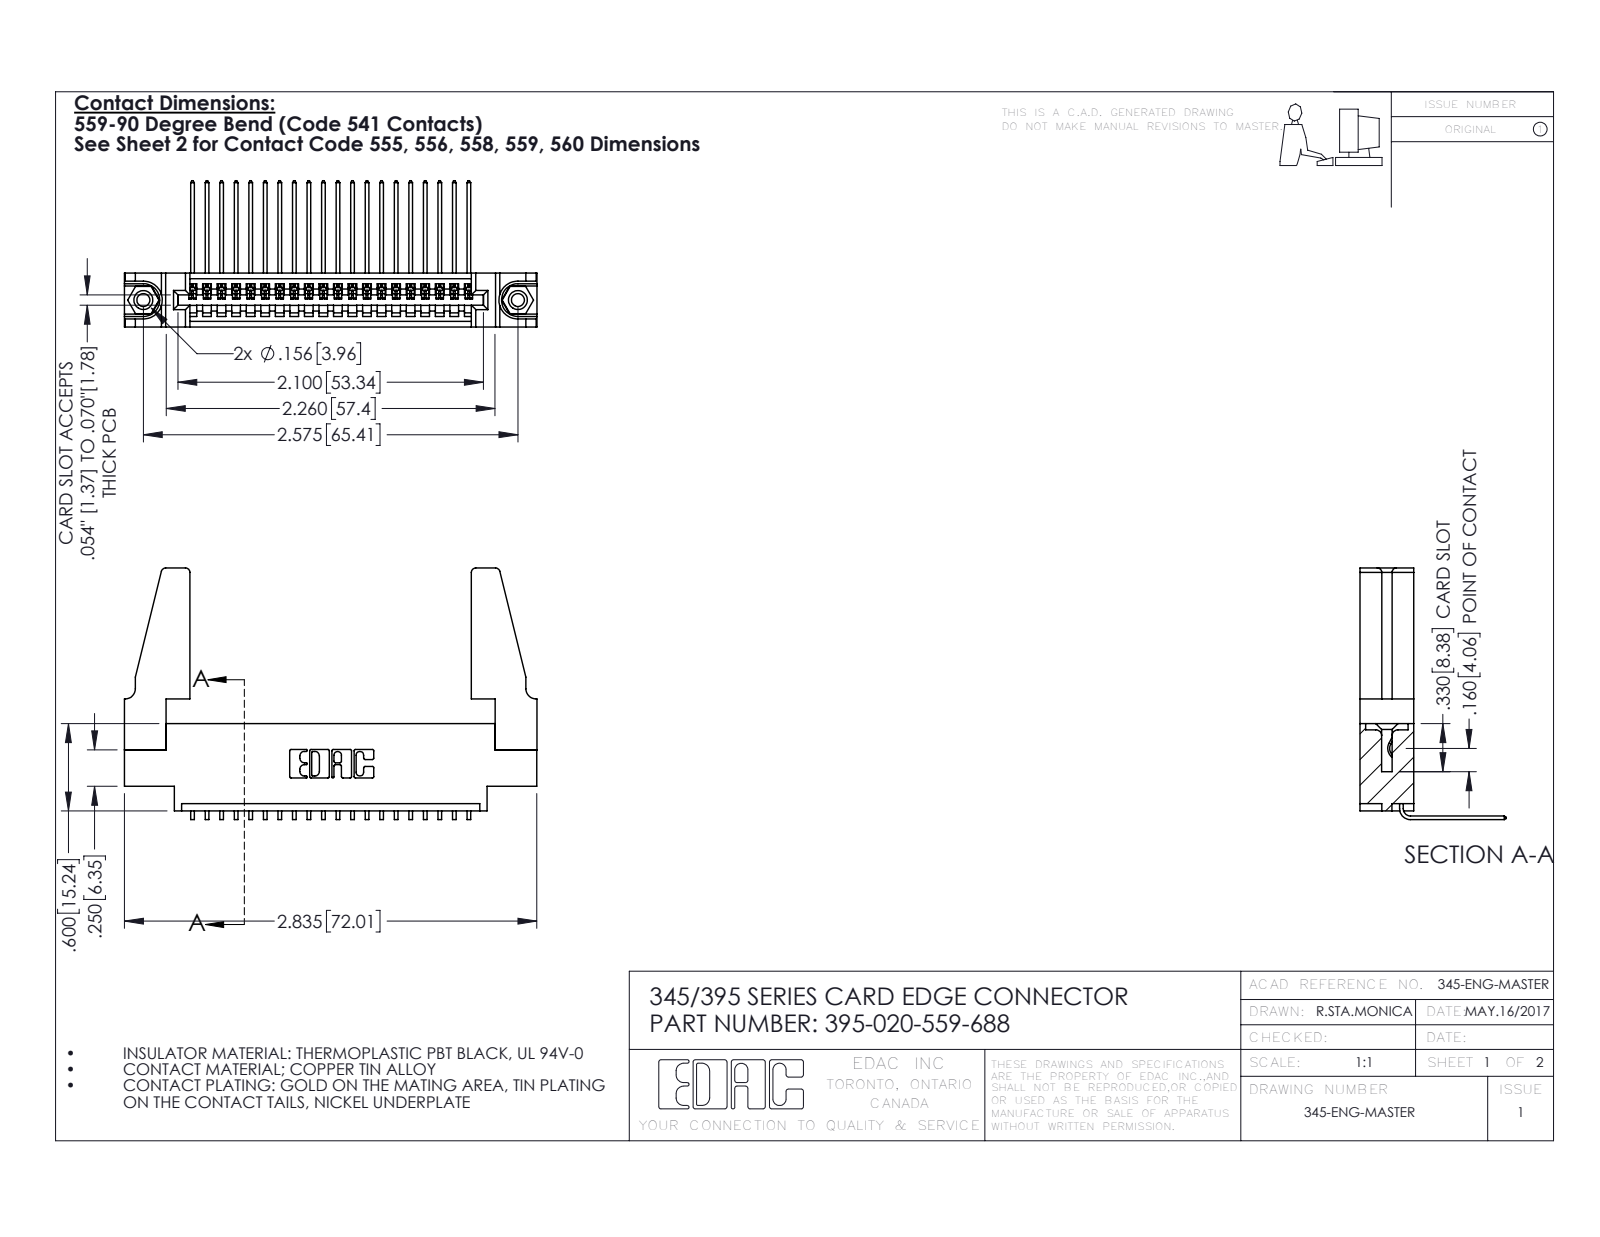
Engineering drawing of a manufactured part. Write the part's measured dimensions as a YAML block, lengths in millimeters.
part_name: "345 Part_0.170 Offset - 0.156 Dia-TH; 395-020-559-688; 345-250-001_345-250-001-102; 345-292-001_558 559 Tail - 1 (+1 more)"
step_written_by: "SolidWorks 2016 (CONFIG_CONTROL_DESIGN)"
units: millimeters
bodies: {solids: 25, faces: 1454, planar: 996, cylindrical: 442, other: 16}
overall_size: [72, 43.9, 25.5]
volume: 9870
surface_area: 12140
round_holes:
  - {diameter: 2.3, count: 2}
  - {diameter: 3.2, count: 2}
  - {diameter: 4, count: 2}
  - {diameter: 1.6, count: 1}
round_bosses_or_shafts:
  - {diameter: 3.9, count: 2}
partial_cylinders:
  - {radius: 0.2, count: 40}
  - {radius: 0.3, count: 22}
  - {radius: 0.8, count: 8}
  - {radius: 0.2, count: 6}
  - {radius: 0.8, count: 6}
  - {radius: 0.7, count: 3}
  - {radius: 0.8, count: 2}
  - {radius: 1, count: 2}
face_to_face_distances: [9.4, 1.8, 7.6, 5.1, 2.5, 6.9, 0.6, 5.7, 4.4, 3.8]
hole_center_spacings: [6.9, 59.5, 65.4]
